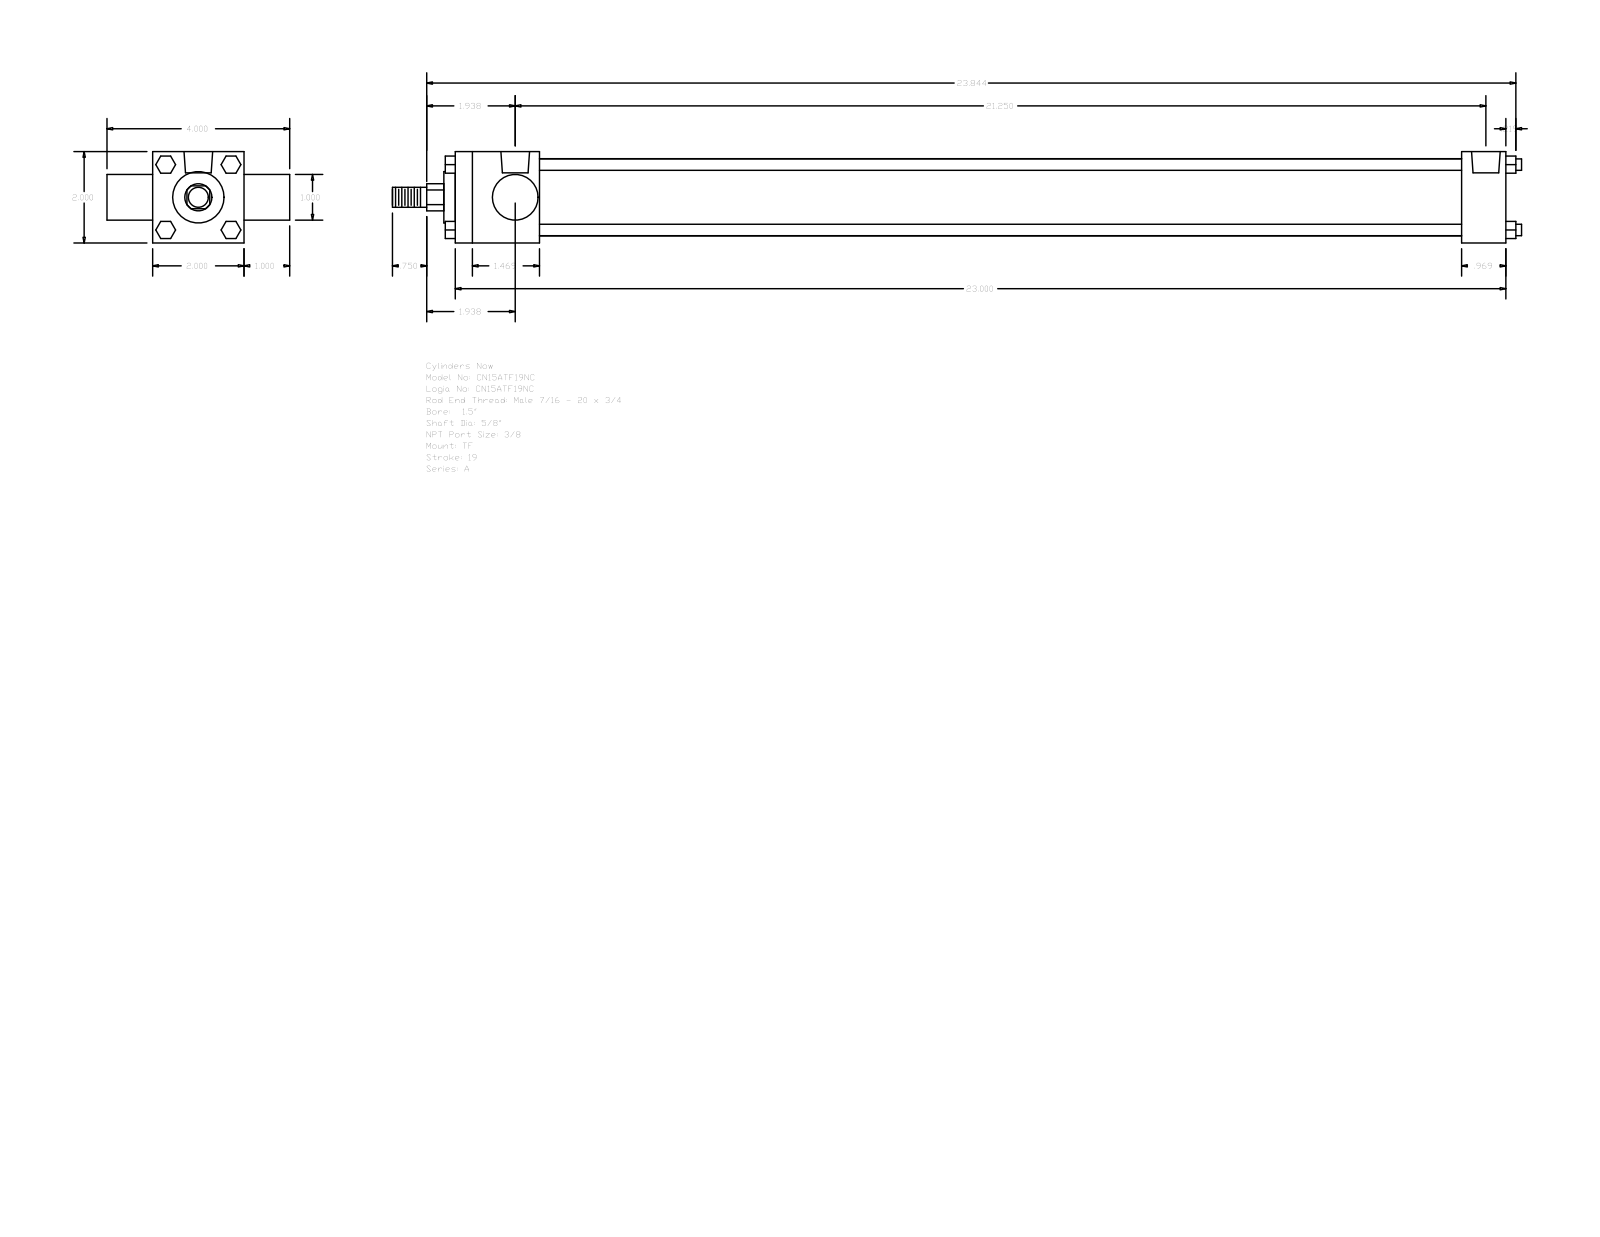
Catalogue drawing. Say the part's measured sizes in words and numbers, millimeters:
The part is named "A_TF__0150_0.625". Its 3-D file was written by "GSSL Pune (CONFIG_CONTROL_DESIGN)". It is 0 solids with 120 faces: 92 planar, 28 cylindrical and 0 other. Overall it measures 627.86 by 101.6 by 50.8 millimeters. Round holes: 3 of diameter 5.56, 2 of diameter 15.93. Round bosses or shafts: 4 of diameter 6.35, 1 of diameter 42.93, 1 of diameter 28.57, 1 of diameter 25.4, 1 of diameter 15.88, 1 of diameter 11.11. Partial cylindrical surfaces (rounded edges, fillets, slot ends): 1 of radius 7.54. The main face-to-face distances are 50.8, 584.2, 25.4, 76.2, 46.83, 559.59, 512.76, 537.37, 24.61, 101.6. The hole center spacings are 3.97, 535.78, 531.81, 539.75.
